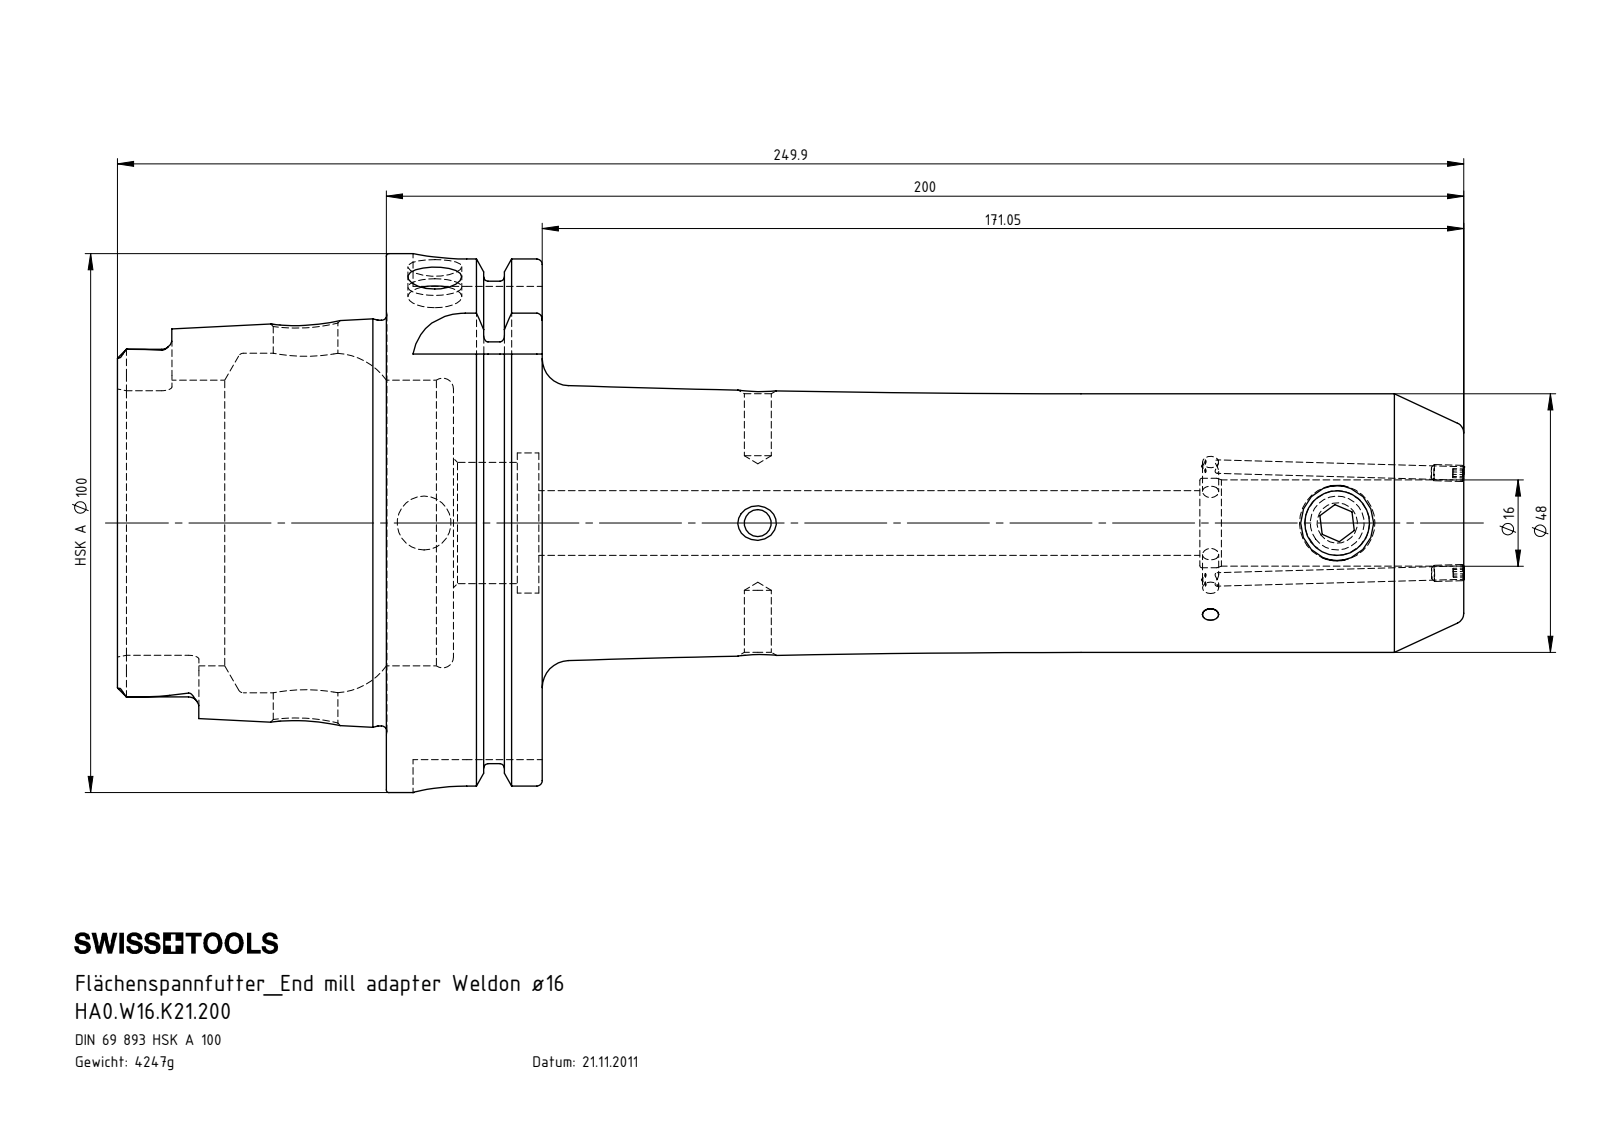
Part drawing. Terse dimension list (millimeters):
name: HA0-W16.K21.200
written by: SolidWorks 2012 (AUTOMOTIVE_DESIGN)
unit: mm
bodies: 1 solid, 230 faces (45 planar, 79 cylindrical, 106 other)
size: 249.9 × 100 × 100
volume: 538 779 mm³; area: 83 507 mm²
holes: 3× ⌀10, 3× ⌀12, 2× ⌀2.5, 2× ⌀5, 1× ⌀3, 1× ⌀16, 1× ⌀16.6, 1× ⌀22.5, 1× ⌀26, 1× ⌀53, 1× ⌀63
bosses: 1× ⌀100, 1× ⌀91.95, 1× ⌀75.26, 1× ⌀48
rounds: 6× R1.9, 4× R4.88, 4× R10
face distances: 28.95, 12.45, 16.5, 49.9, 62.35, 78.85, 249.9, 200, 187.55, 171.05
hole spacings: 61.95, 83.95, 107.55, 169.5
